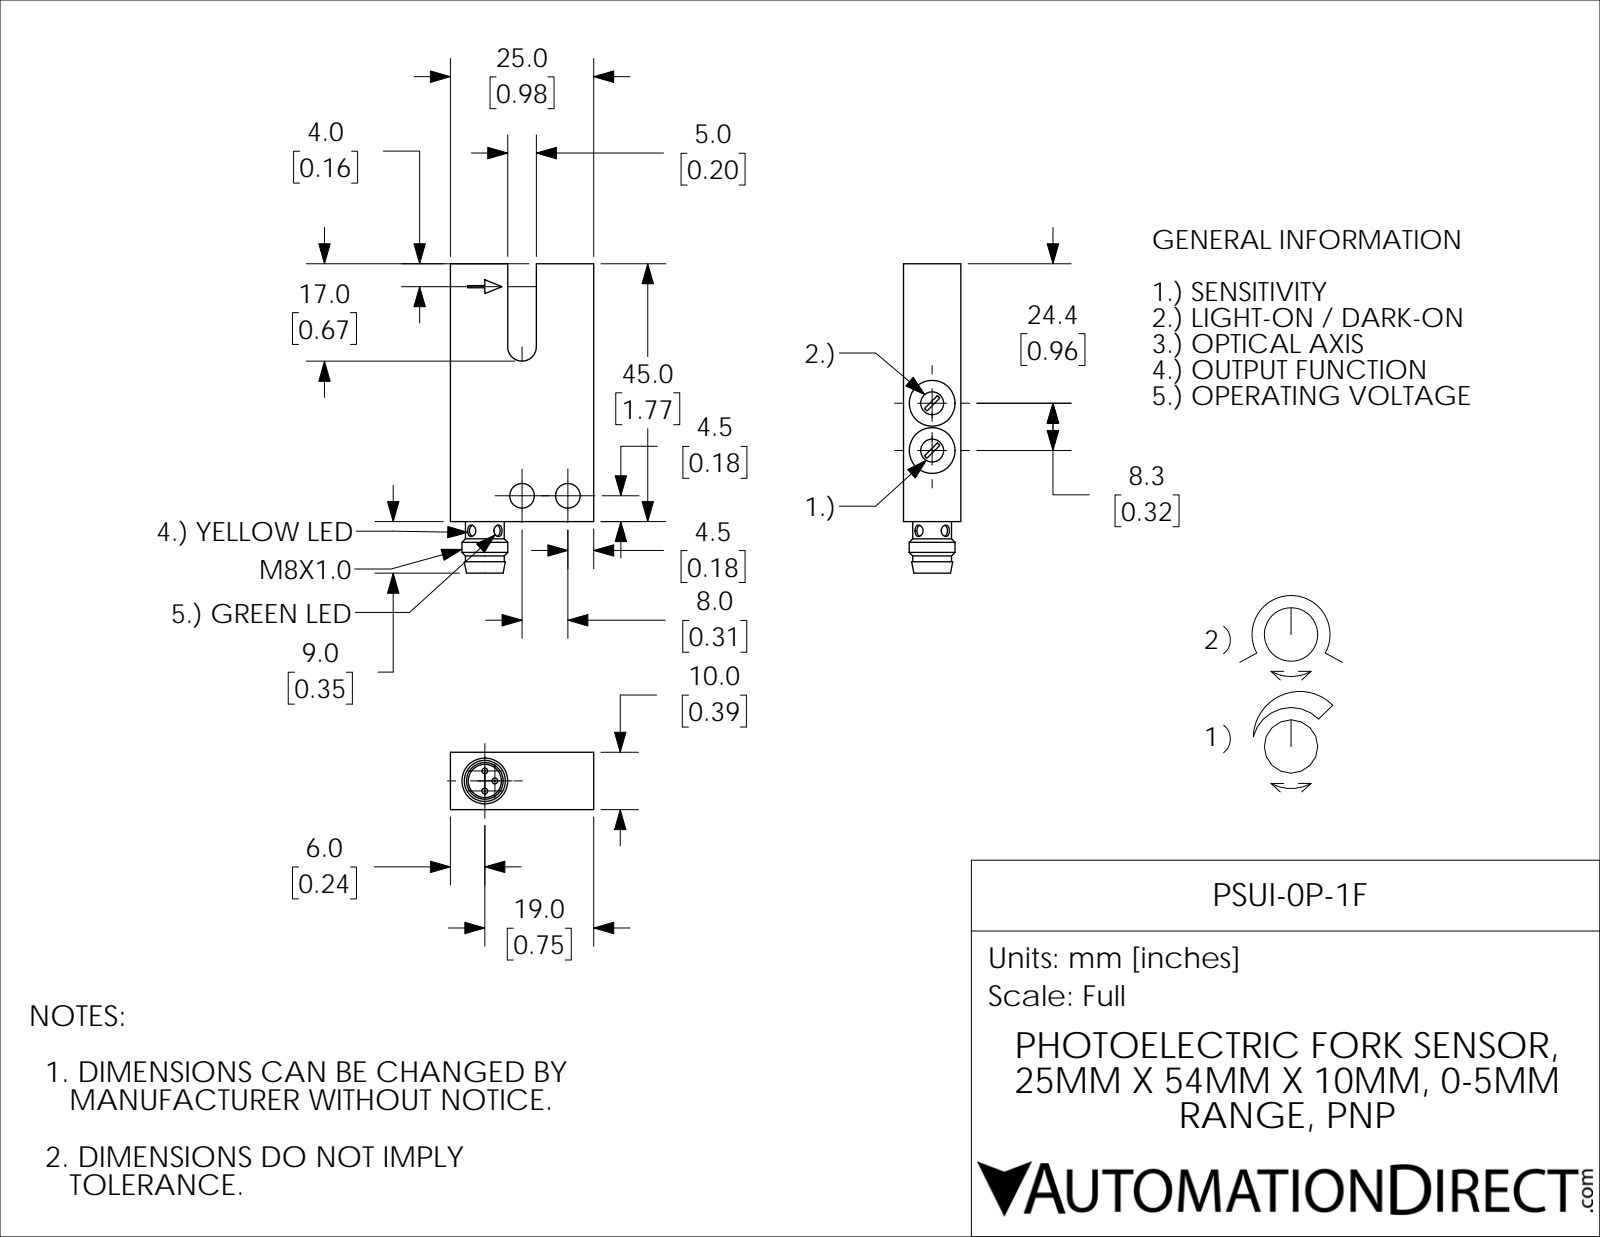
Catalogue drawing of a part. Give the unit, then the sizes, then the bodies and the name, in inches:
Units: inches
Overall size (bounding box): 2.126 × 0.984 × 0.394
Round holes (diameter × count): ⌀0.079 ×2, ⌀0.157 ×2, ⌀0.169 ×2, ⌀0.315 ×2, ⌀0.228 ×1
Round bosses / shafts (diameter × count): ⌀0.039 ×3, ⌀0.315 ×1, ⌀0.267 ×1
Partial cylindrical surfaces — rounded edges, fillets, slot ends (radius × count): R0.063 ×2, R0.098 ×1
Main face-to-face distances: 0.394, 0.984, 0.591, 1.772, 0.197, 0.39, 0.98, 0.587, 0.157, 1.929
Hole centre spacings: 0.315, 0.325
Volume: 0.632 in³ · Surface area: 6.805 in²
Bodies: 1 solid, 65 faces (37 planar, 22 cylindrical, 6 other)
Part name (STEP PRODUCT): PSUI-0P-1F
STEP written by: SolidWorks 2017 (AUTOMOTIVE_DESIGN)
